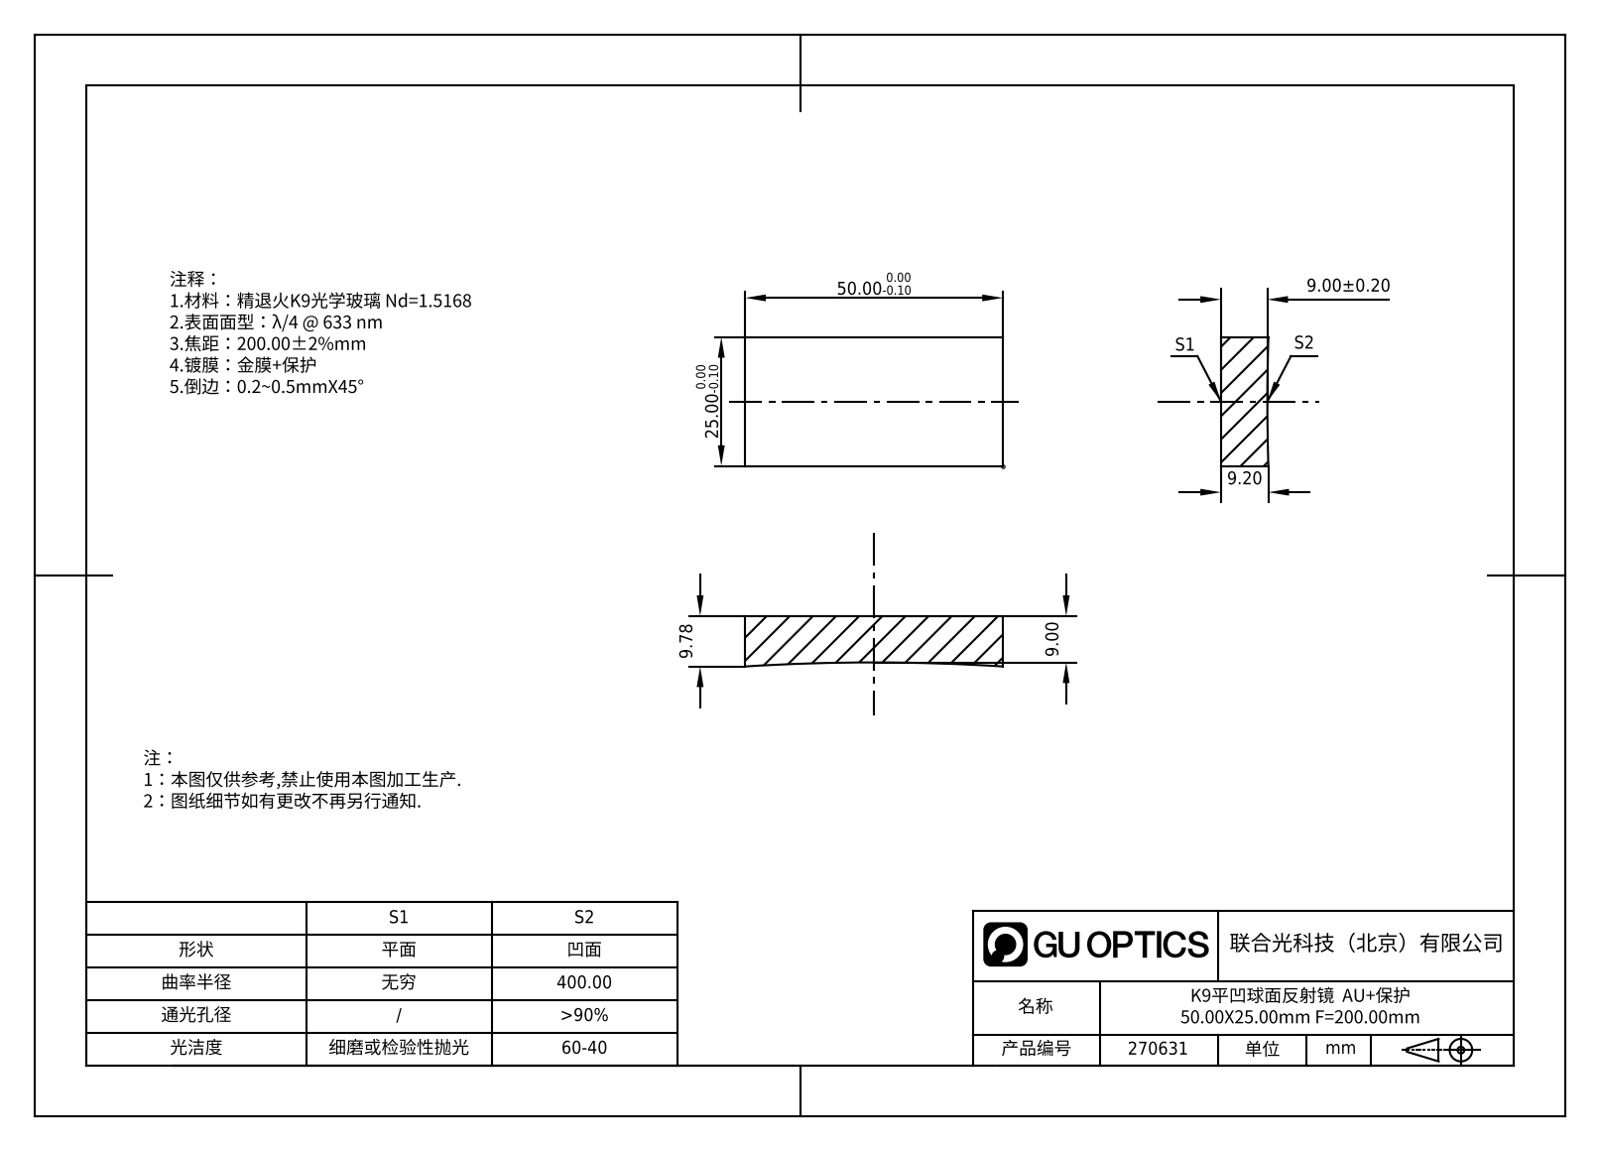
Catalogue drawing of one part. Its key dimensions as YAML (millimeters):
part_name: "GM13-50x25-200"
step_written_by: "SolidWorks 2022 (AUTOMOTIVE_DESIGN)"
units: millimeters
bodies: {solids: 1, faces: 7, planar: 5, cylindrical: 0, other: 2}
overall_size: [50, 25, 9.98]
volume: 11657
surface_area: 3939
face_to_face_distances: [25, 50]
